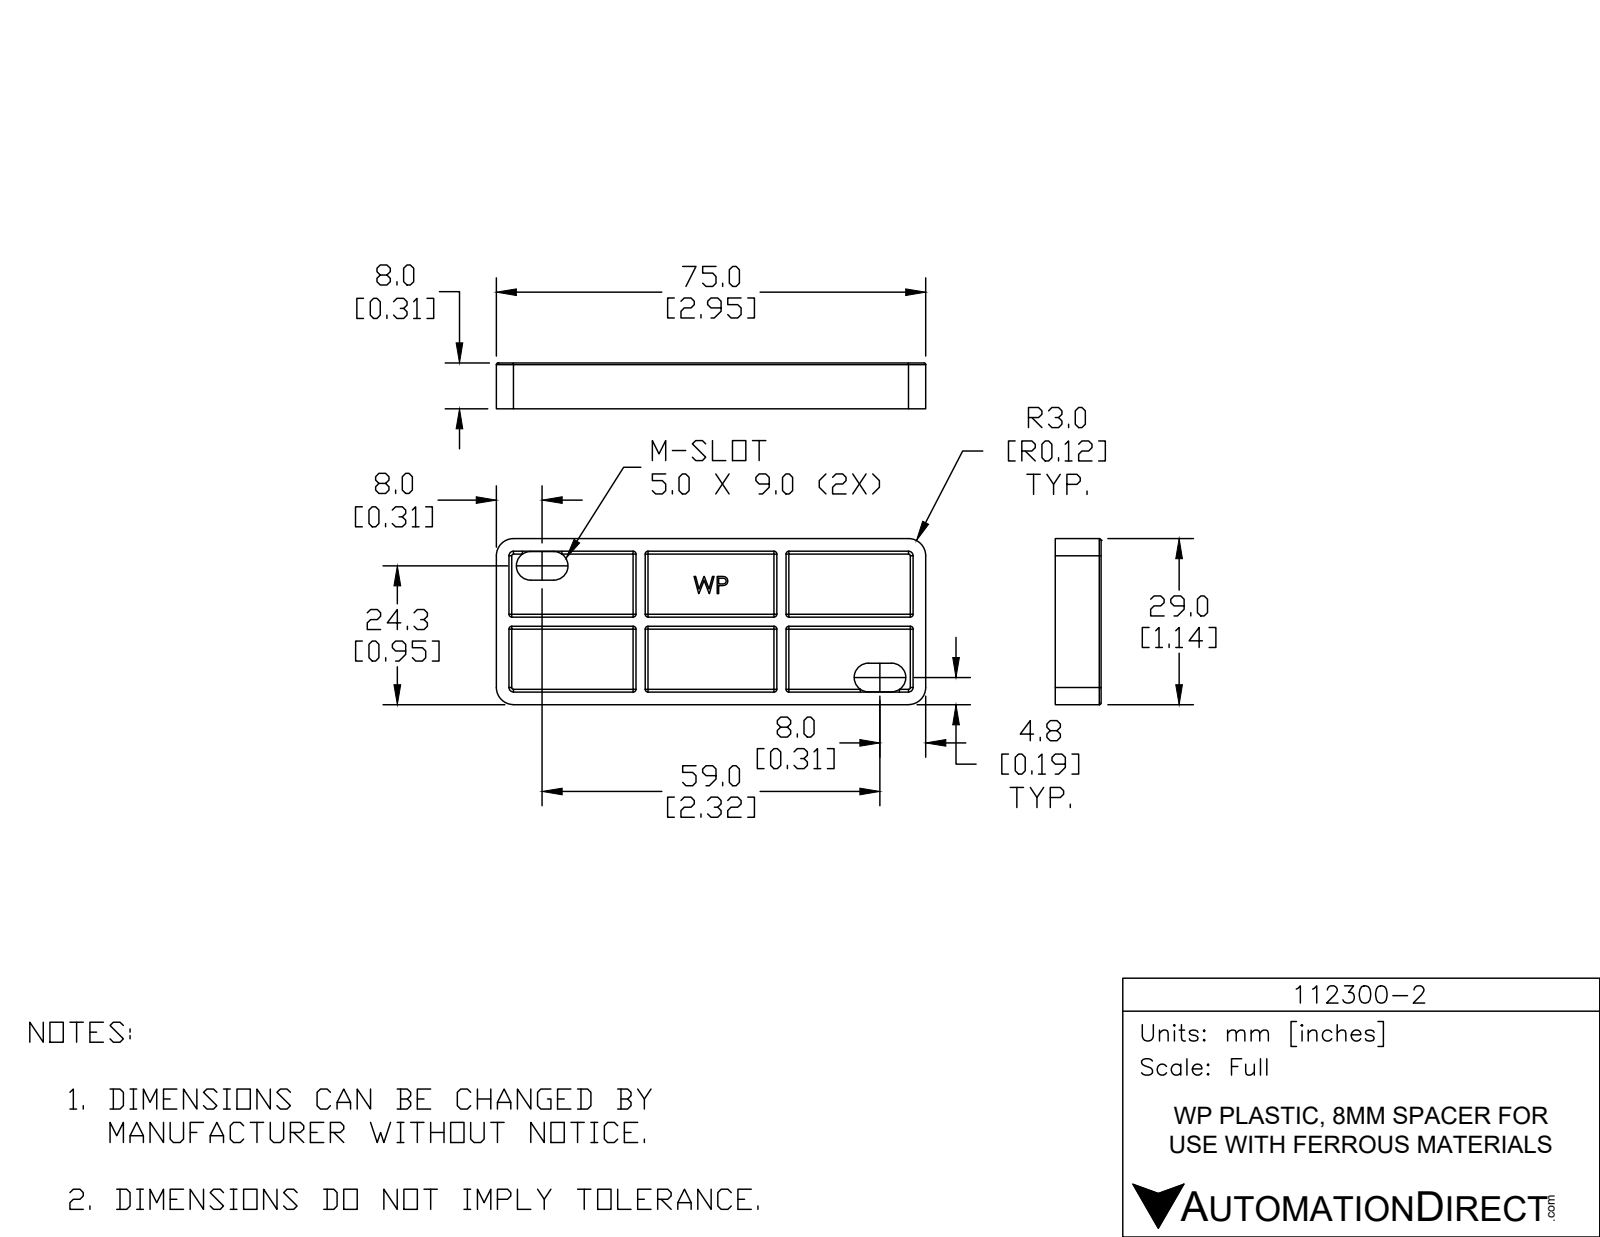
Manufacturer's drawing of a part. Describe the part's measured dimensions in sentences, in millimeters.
The part is named "112-WP Spacer". Its 3-D file was written by "SolidWorks 2018 (CONFIG_CONTROL_DESIGN)". It is 1 solid with 178 faces: 68 planar, 66 cylindrical and 44 other. Overall it measures 75 by 29 by 8 millimeters. Its volume is 9 347 cubic millimeters and its surface area 7 825 square millimeters. Partial cylindrical surfaces (rounded edges, fillets, slot ends): 32 of radius 0.5, 4 of radius 0.3, 4 of radius 0.8, 4 of radius 2.5, 4 of radius 3. The main face-to-face distances are 3, 2.2, 5, 8, 13.7, 15.3, 26.8, 11.5, 13.1, 29.
